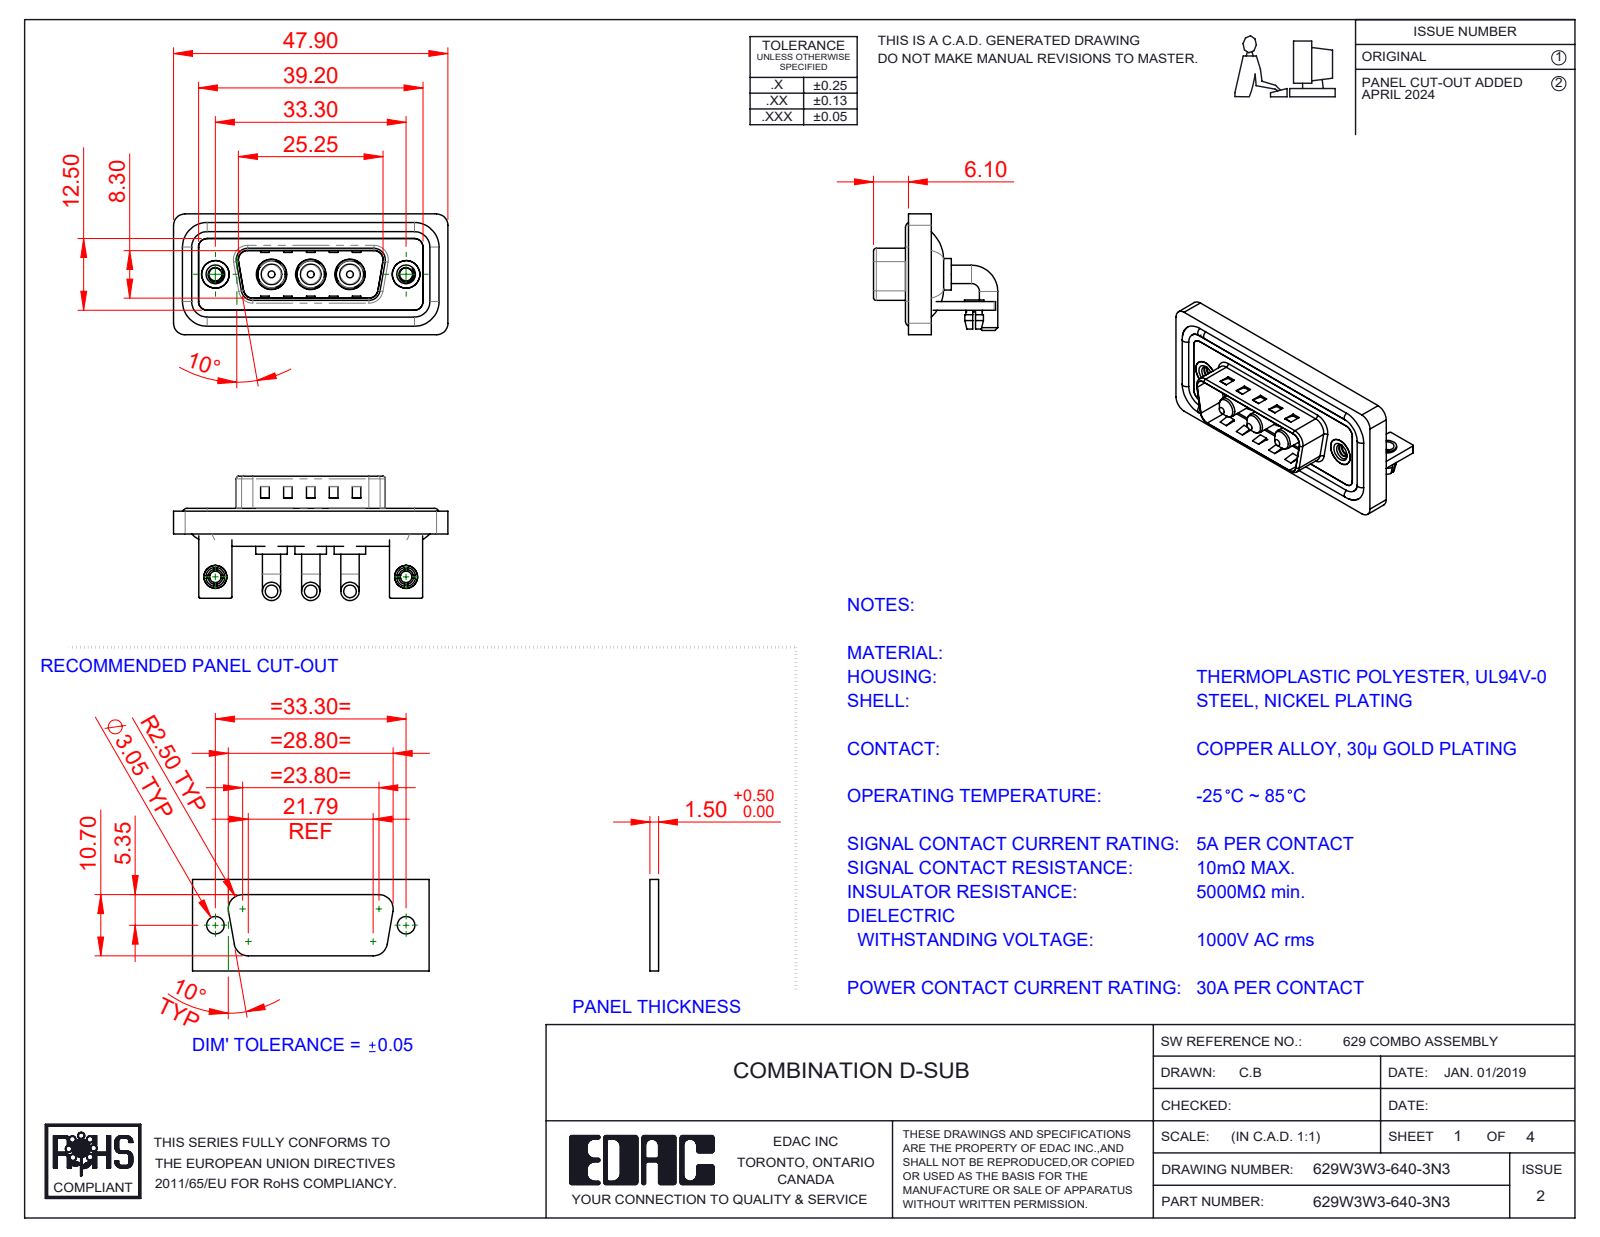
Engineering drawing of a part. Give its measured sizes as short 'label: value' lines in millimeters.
name: 629Combo Housing_3W3; 629Combo Stabilizer Bracket; 629Combo Waterproof Housing_15 Contacts; 629W3W3-640-3N3 (+5 more)
written by: SolidWorks 2023 (CONFIG_CONTROL_DESIGN)
unit: mm
bodies: 17 solids, 708 faces (275 planar, 297 cylindrical, 136 other)
size: 47.9 × 21.7 × 21.1
volume: 6 176 mm³; area: 9 889 mm²
holes: 3× ⌀4.85, 3× ⌀5.3, 2× ⌀2, 2× ⌀2.26, 2× ⌀2.5, 2× ⌀3.2, 2× ⌀4, 2× ⌀4.8, 2× ⌀5
bosses: 6× ⌀3.2, 4× ⌀1.6, 3× ⌀5.5, 3× ⌀5.2, 3× ⌀4.75, 3× ⌀3.75, 3× ⌀3.6, 2× ⌀4.9
rounds: 21× R2, 18× R1.5, 16× R0.25, 9× R0.5, 8× R1.6, 4× R0.6, 4× R0.65, 4× R0.9
face distances: 0.4, 1.5, 0.8, 2.9, 1.1, 2.1, 3.7, 1.6, 1.2, 4.5
hole spacings: 6.85, 9.8, 16.65, 23.5, 33.3, 13.7
